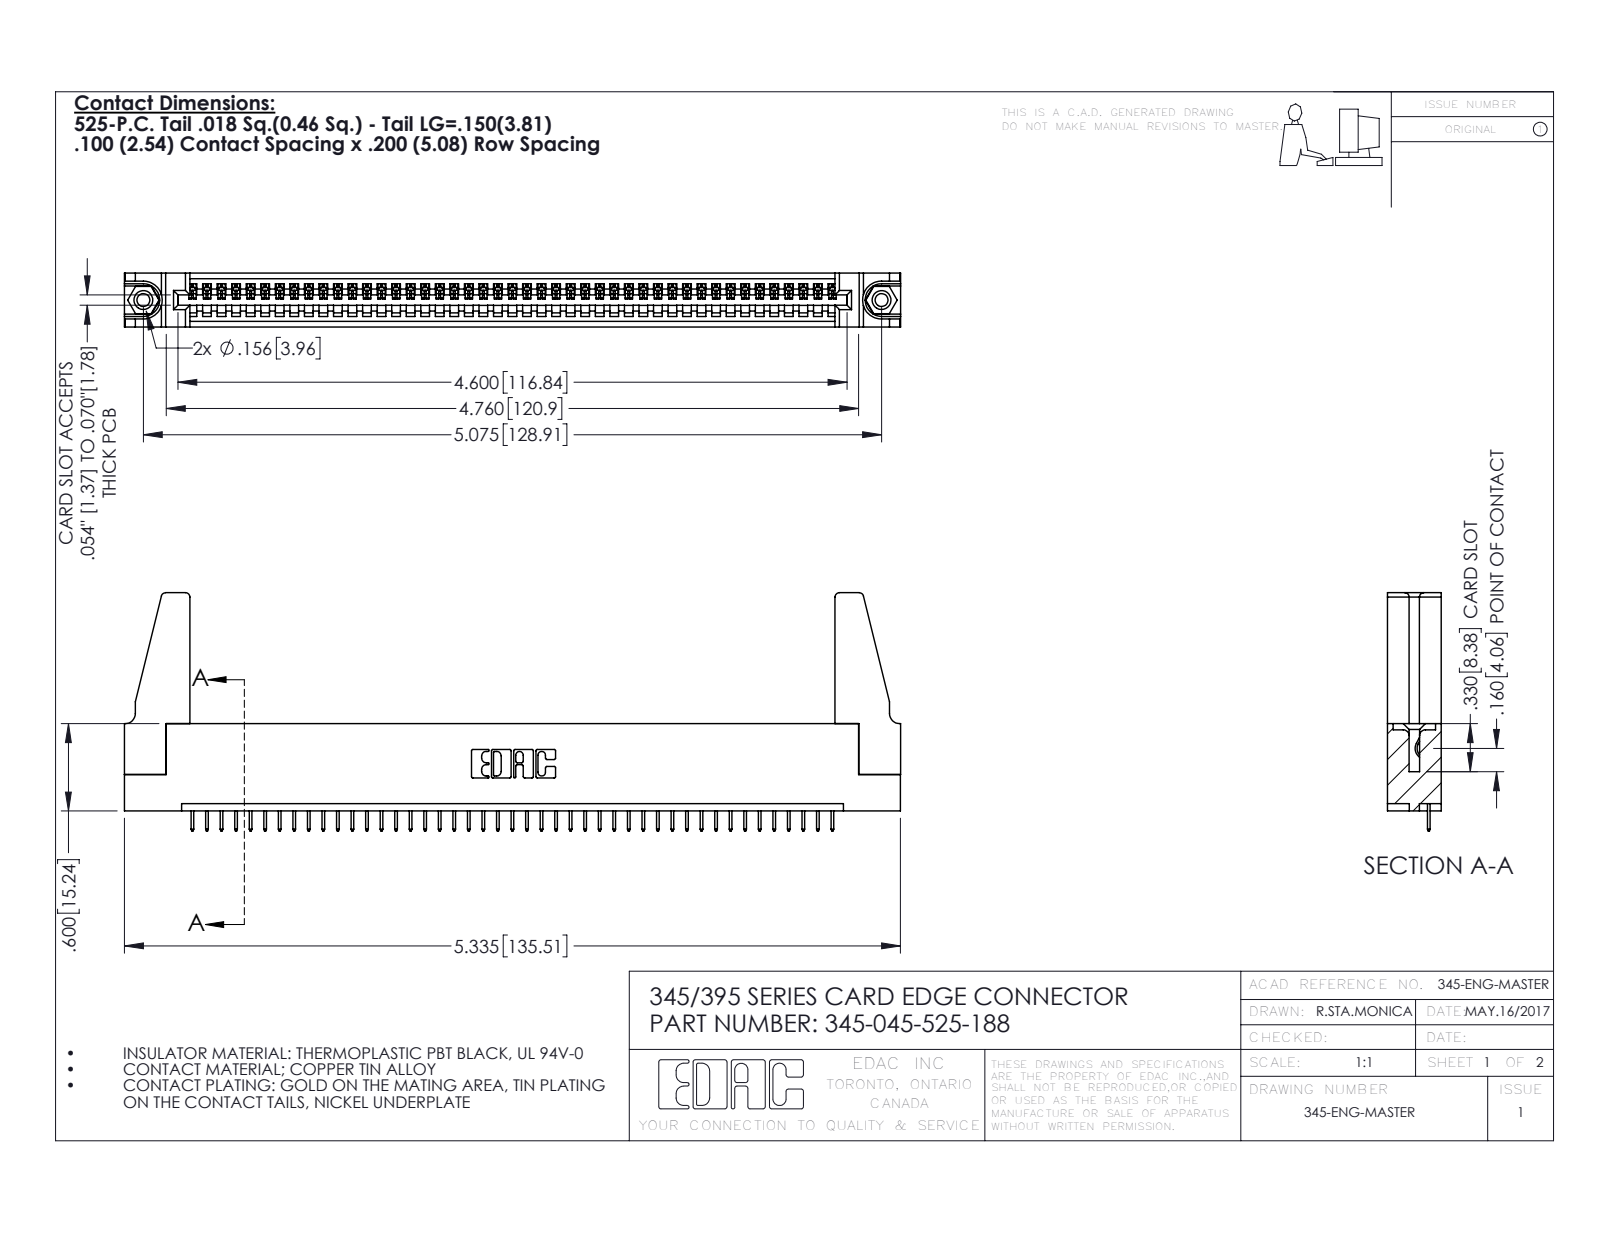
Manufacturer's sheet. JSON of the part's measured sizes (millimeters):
{"part_name": "345 Part_Flush Mounting Lugs - 0.156 Dia-TH; 345-045-525-188; 345-220-078_345-220-088; 345-292-001_345-293-125 (+1 more)", "step_written_by": "SolidWorks 2020 (CONFIG_CONTROL_DESIGN)", "units": "millimeters", "bodies": {"solids": 50, "faces": 3040, "planar": 2222, "cylindrical": 802, "other": 16}, "overall_size": [135.5, 41.6, 9.4], "volume_mm3": 16000, "surface_area_mm2": 19450, "round_holes": [[2.3, 2], [3.2, 2], [4, 2], [1.6, 1]], "round_bosses_or_shafts": [[3.9, 2]], "partial_cylinders_radius": [[0.2, 90], [0.3, 22], [0.8, 8], [0.2, 6], [0.8, 6], [0.7, 3], [0.8, 2], [1, 2]], "face_to_face_distances": [1.8, 9.4, 7.6, 5.1, 2.5, 6.9, 0.6, 5.7, 1.8, 3.8], "hole_center_spacings": [6.9, 122.9, 128.9]}
